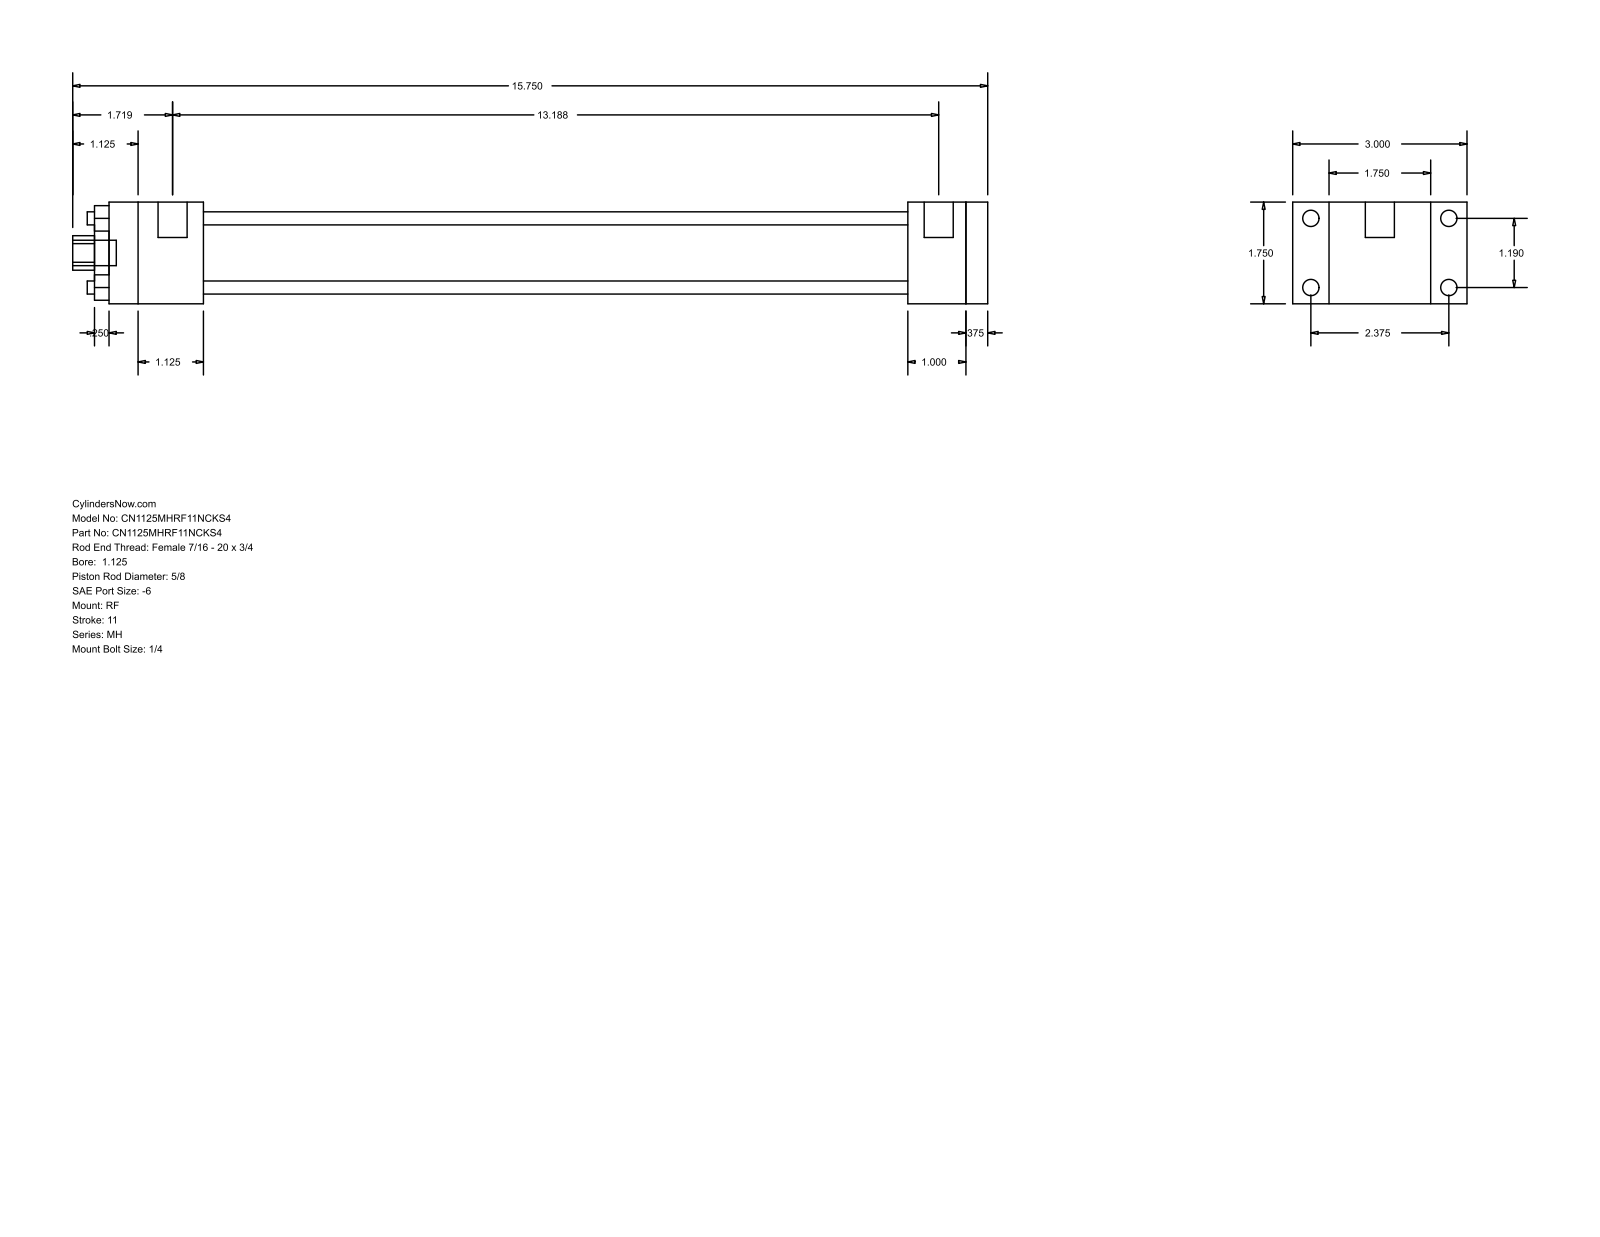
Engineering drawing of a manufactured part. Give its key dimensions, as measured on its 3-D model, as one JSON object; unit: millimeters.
{"part_name": "MH_RF__0112_0.625", "step_written_by": "GSSL Pune (CONFIG_CONTROL_DESIGN)", "units": "millimeters", "bodies": {"solids": 0, "faces": 92, "planar": 64, "cylindrical": 28, "other": 0}, "overall_size": [400.05, 76.2, 44.45], "round_holes": [[5.71, 4], [15.88, 1], [28.57, 1], [34.92, 1]], "round_bosses_or_shafts": [[7.14, 4], [5.56, 4], [12.7, 2], [11.11, 1]], "partial_cylinders_radius": [[7.54, 1]], "face_to_face_distances": [44.46, 9.53, 384.17, 15.87, 333.37, 342.9, 307.97, 25.4, 34.93, 41.27], "hole_center_spacings": [21.37, 30.22, 42.74]}
